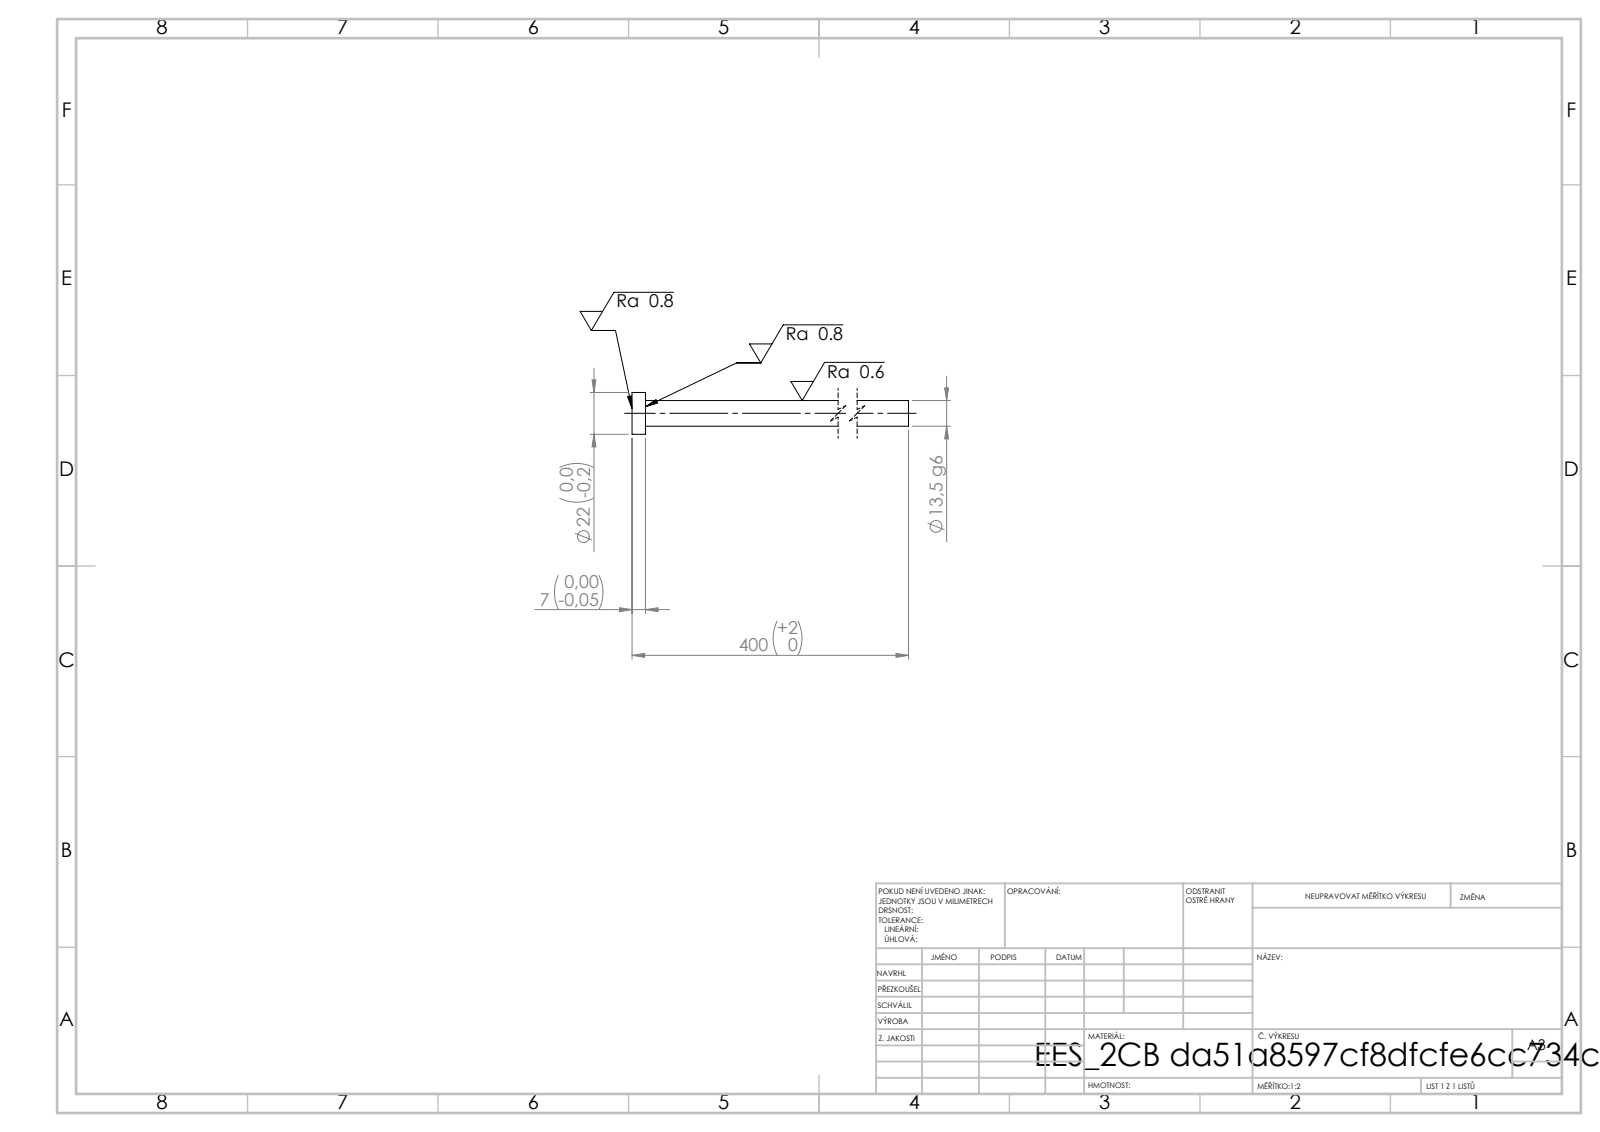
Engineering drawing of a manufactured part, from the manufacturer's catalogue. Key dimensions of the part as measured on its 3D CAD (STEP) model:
STEP written by: SolidWorks 2019 (CONFIG_CONTROL_DESIGN)
Units: millimetres
Bodies: 1 solid, 7 faces (3 planar, 4 cylindrical, 0 other)
Overall size (bounding box): 400 × 22 × 22
Volume: 58 914 mm³ · Surface area: 17 912 mm²
Round bosses / shafts (diameter × count): ⌀22 ×1, ⌀13.5 ×1
Main face-to-face distances: 7, 400, 393
